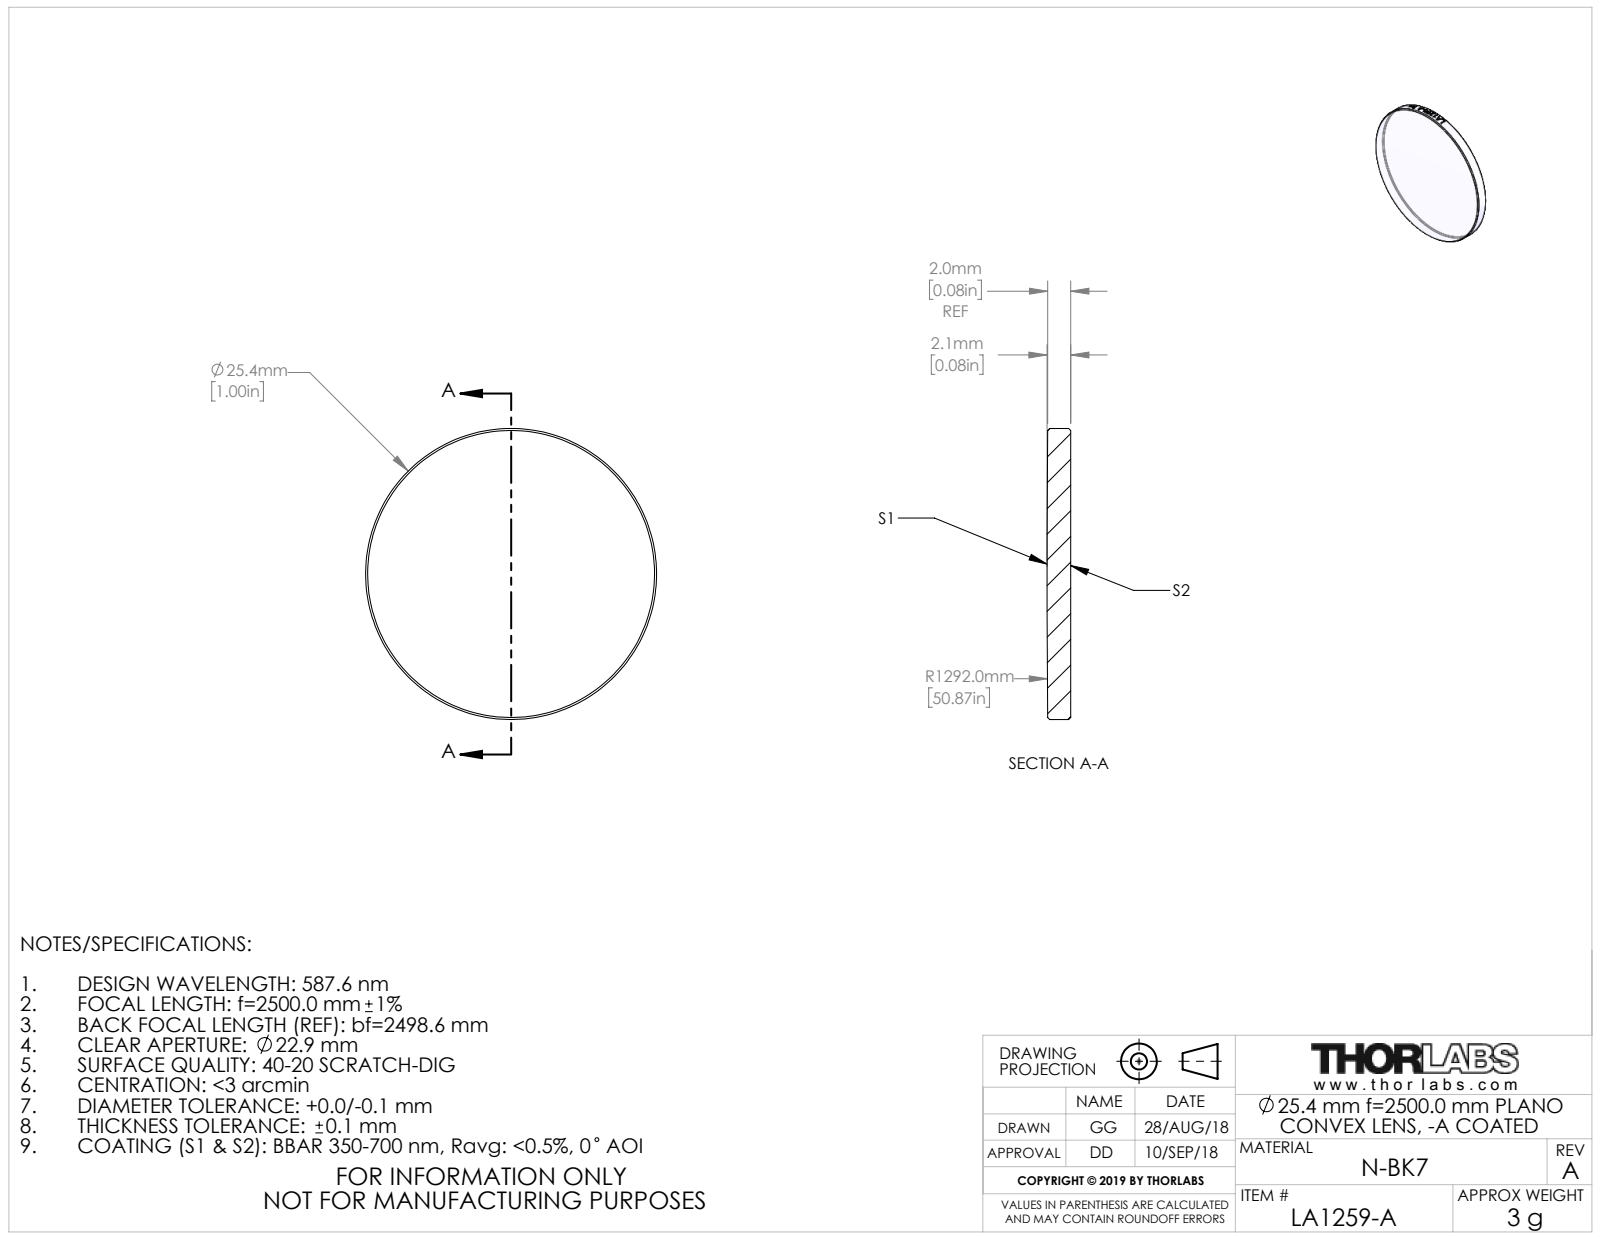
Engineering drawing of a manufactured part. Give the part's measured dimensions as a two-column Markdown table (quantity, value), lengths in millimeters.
| quantity | value |
| --- | --- |
| part name | TTN162131-E0W |
| STEP written by | SolidWorks 2018 (CONFIG_CONTROL_DESIGN) |
| units | millimeters |
| bodies | 1 solid, 25 faces (1 planar, 18 cylindrical, 6 other) |
| overall size | 25.4 × 25.4 × 2.06 |
| volume | 1 026 mm³ |
| surface area | 1 156 mm² |
| round bosses / shafts (diameter × count) | 25.4 × 1 |
